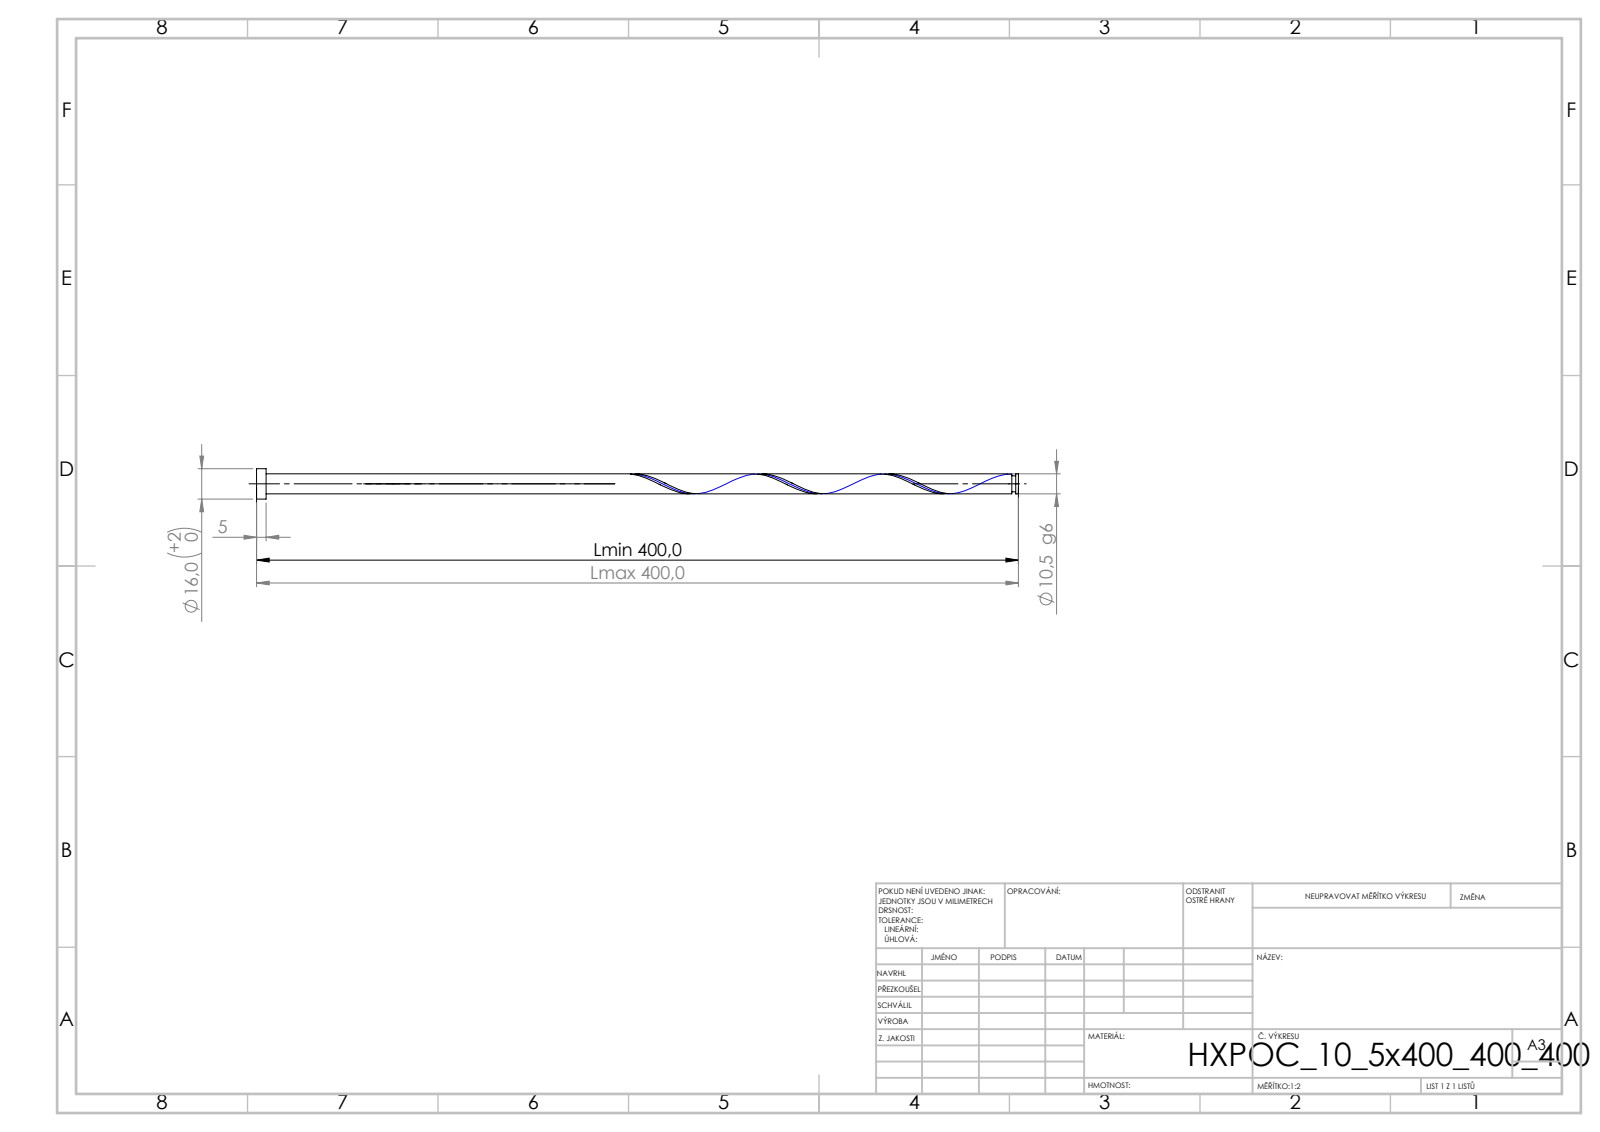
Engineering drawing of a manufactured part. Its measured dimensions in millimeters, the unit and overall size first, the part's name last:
Units: millimetres
Overall size (bounding box): 400 × 16 × 16
Round bosses / shafts (diameter × count): ⌀16 ×1, ⌀10.5 ×1, ⌀8.4 ×1
Main face-to-face distances: 5, 400, 395, 398.58, 393.58, 1.42, 396.48, 391.48, 2.1, 3.52
Volume: 34 811 mm³ · Surface area: 13 962 mm²
Bodies: 1 solid, 21 faces (6 planar, 14 cylindrical, 1 other)
STEP written by: SolidWorks 2019 (CONFIG_CONTROL_DESIGN)
